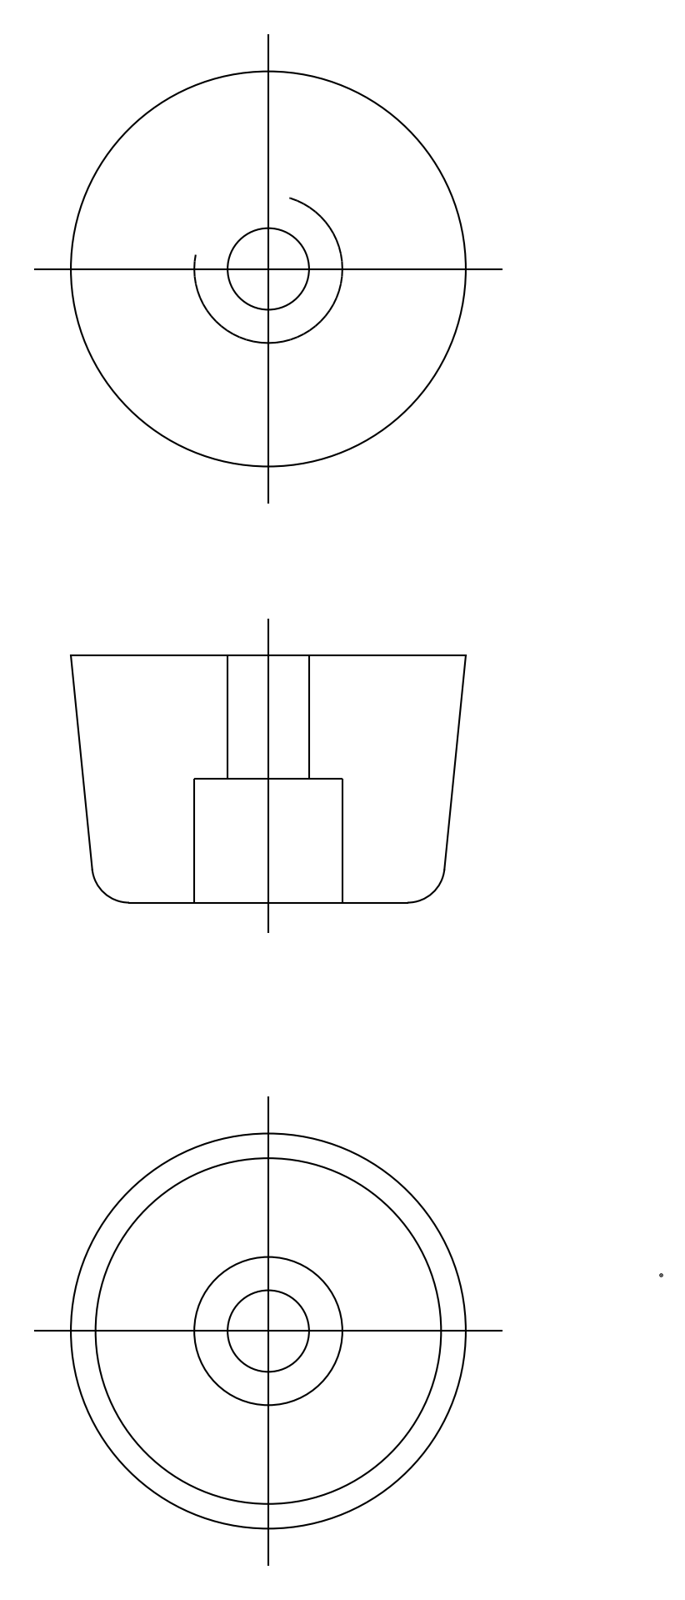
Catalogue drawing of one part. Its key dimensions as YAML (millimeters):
step_written_by: "spGate 19.8.4 (****-****-****-****) (AUTOMOTIVE_DESIGN)"
units: millimeters
bodies: {solids: 1, faces: 11, planar: 3, cylindrical: 4, other: 4}
overall_size: [16, 16, 10]
volume: 1573
surface_area: 935
round_holes:
  - {diameter: 3.3, count: 1}
  - {diameter: 6, count: 1}
face_to_face_distances: [10, 5]
